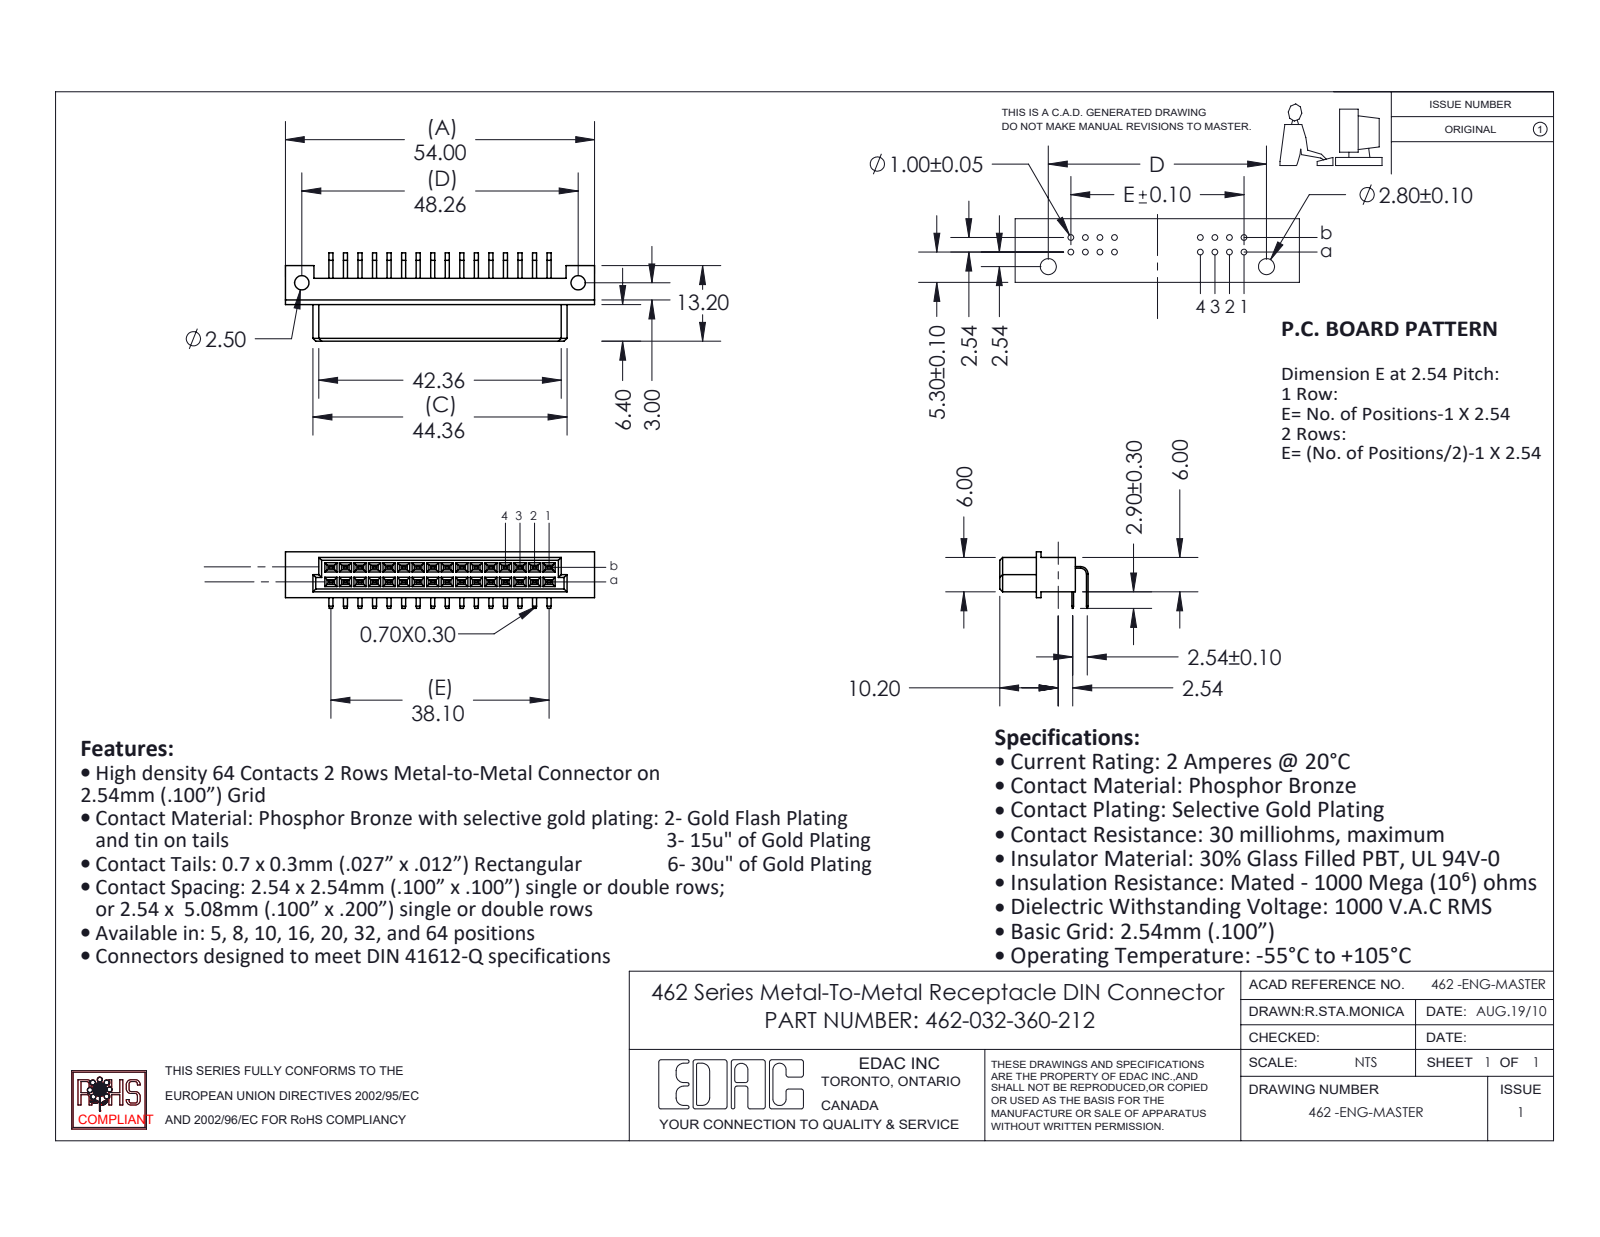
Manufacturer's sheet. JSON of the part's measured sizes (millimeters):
{"part_name": "462 Part_32; 462-290-1; 462-032-360-212; 462-290-2", "step_written_by": "SolidWorks 2020 (CONFIG_CONTROL_DESIGN)", "units": "millimeters", "bodies": {"solids": 33, "faces": 899, "planar": 831, "cylindrical": 68, "other": 0}, "overall_size": [54, 15.43, 9.9], "volume_mm3": 3117, "surface_area_mm2": 4074, "round_holes": [[2.5, 2]], "partial_cylinders_radius": [[1.02, 2], [1.32, 2]], "face_to_face_distances": [2.54, 6, 0.81, 1.58, 1.88, 4.12, 4.42, 0.56, 0.55, 4.6], "hole_center_spacings": [48.26]}
